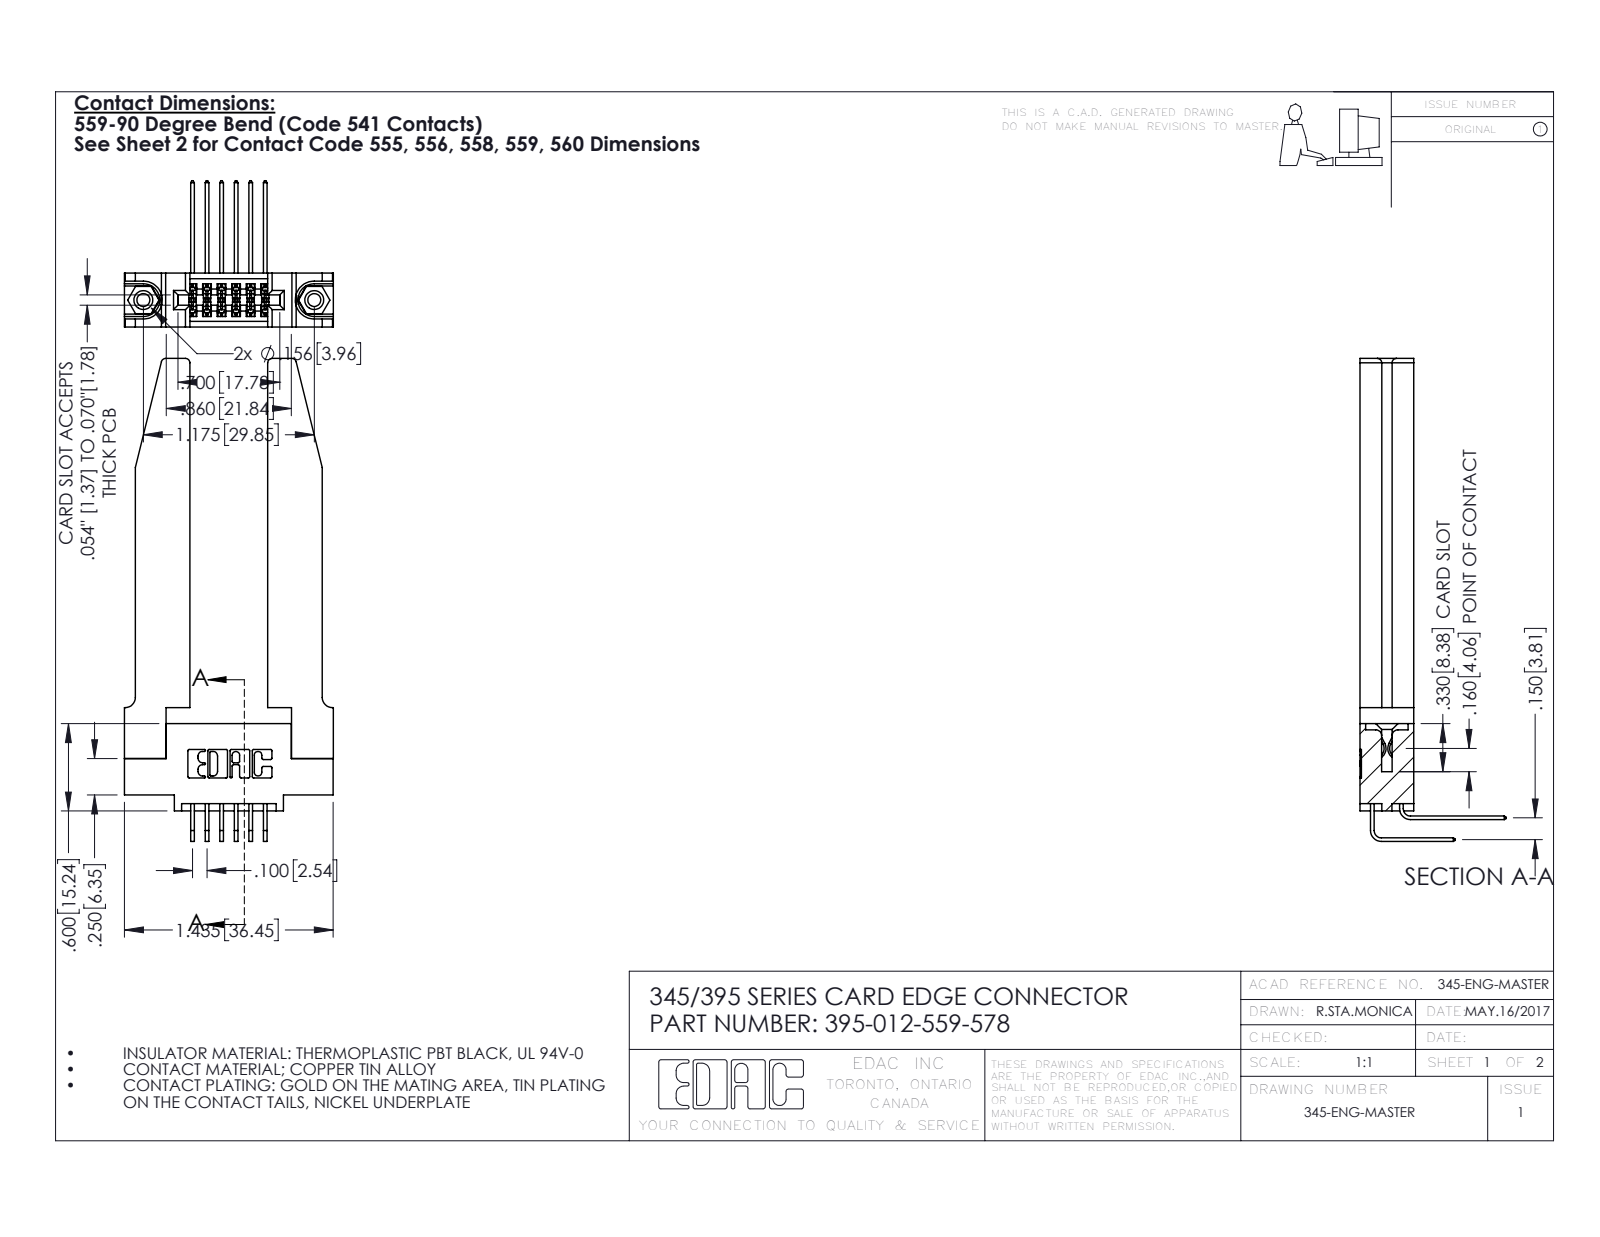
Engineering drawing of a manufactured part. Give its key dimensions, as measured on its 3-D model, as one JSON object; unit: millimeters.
{"part_name": "345-250-001_345-250-001-102; 345-292-001_559 Tail - 2; 395-012-559-578; 345 Part_0.110 Offset - 0.156 Dia-TH (+2 more)", "step_written_by": "SolidWorks 2016 (CONFIG_CONTROL_DESIGN)", "units": "millimeters", "bodies": {"solids": 17, "faces": 988, "planar": 646, "cylindrical": 290, "other": 52}, "overall_size": [84.3, 36.5, 25.5], "volume_mm3": 11000, "surface_area_mm2": 11300, "round_holes": [[2.3, 2], [3.2, 2], [4, 2], [1.6, 1]], "round_bosses_or_shafts": [[3.9, 2]], "partial_cylinders_radius": [[0.3, 22], [0.2, 19], [0.8, 8], [0.2, 6], [0.8, 6], [0.7, 3], [0.4, 2], [0.5, 2]], "face_to_face_distances": [9.4, 3.8, 5.6, 1.8, 3.8, 13.6, 7.6, 2, 5.1, 1.8], "hole_center_spacings": [6.9, 24, 29.8]}
